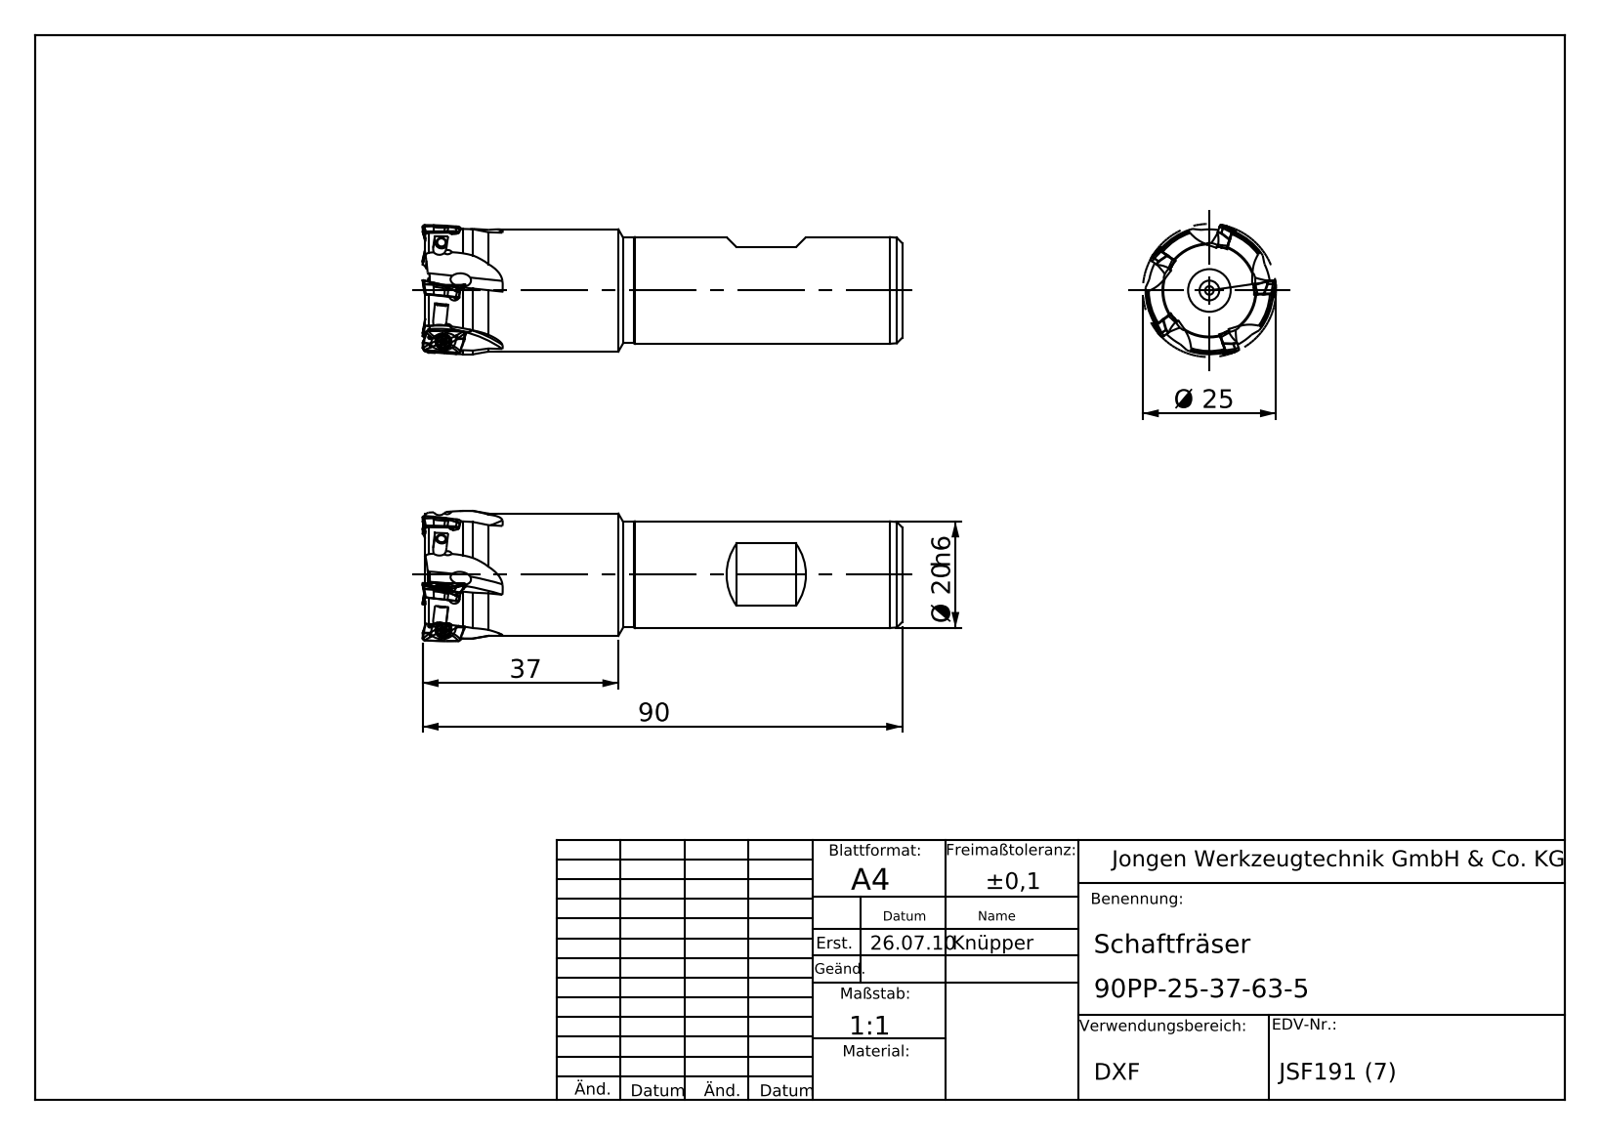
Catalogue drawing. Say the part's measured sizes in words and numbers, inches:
The part is named "90PP-25-37-63-5". Its 3-D file was written by "SolidWorks 2011 (AUTOMOTIVE_DESIGN)". It is 1 solid with 135 faces: 41 planar, 38 cylindrical and 56 other. Overall it measures 3.543 by 0.984 by 0.984 inches. Its volume is 1.847 cubic inches and its surface area 13.7 square inches. Round holes: 5 of diameter 0.098, 1 of diameter 0.063, 1 of diameter 0.157. Round bosses or shafts: 1 of diameter 0.903, 1 of diameter 0.787, 1 of diameter 0.78. Partial cylindrical surfaces (rounded edges, fillets, slot ends): 5 of radius 0.787, 1 of radius 0.472. The main face-to-face distances are 3.524, 3.469, 0.055, 0.079, 0.079.
